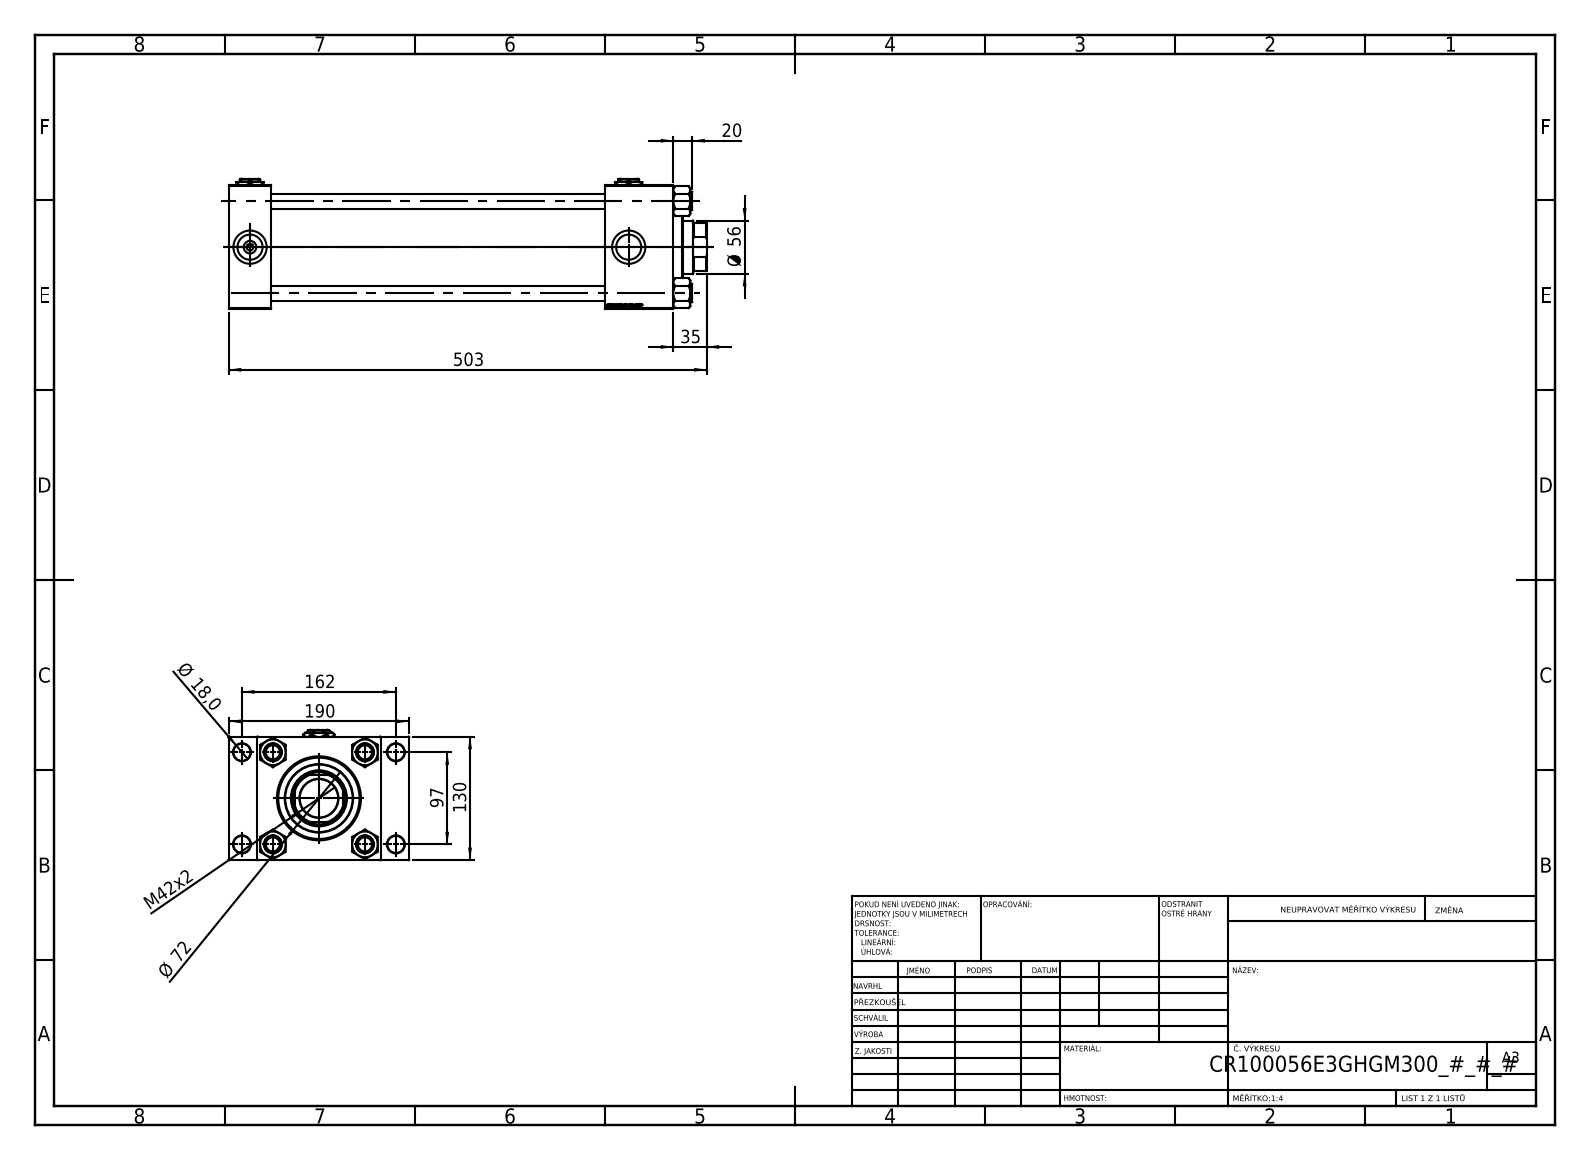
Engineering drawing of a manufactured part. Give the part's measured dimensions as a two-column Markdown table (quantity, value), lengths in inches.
| quantity | value |
| --- | --- |
| part name | Zatka_pro_OIL_PORT; V215_VC_A; NUT_M5_E; V215CR_TYCINKA_E (+2 more) |
| STEP written by | SolidWorks 2019 (CONFIG_CONTROL_DESIGN) |
| units | inches |
| bodies | 13 solids, 1284 faces (593 planar, 97 cylindrical, 594 other) |
| overall size | 19.803 × 7.48 × 5.394 |
| volume | 242.1 in³ |
| surface area | 1 040 in² |
| round holes (diameter × count) | 0.63 × 4, 0.709 × 4, 1.041 × 4, 1.378 × 4, 0.276 × 3, 1.594 × 1, 2.205 × 1, 2.323 × 1, 2.992 × 1, 3.366 × 1, 3.937 × 1 |
| round bosses / shafts (diameter × count) | 0.748 × 4, 4.173 × 1, 2.835 × 1 |
| partial cylindrical surfaces (radius × count) | 1.063 × 1 |
| main face-to-face distances | 5.118, 1.772, 18.425, 16.654, 1.181, 6.299, 15.591, 13.819, 2.835, 3.78 |
| hole center spacings | 1.281, 2.698, 3.717, 3.815, 4.026, 5.096, 6.367, 3.819 |
